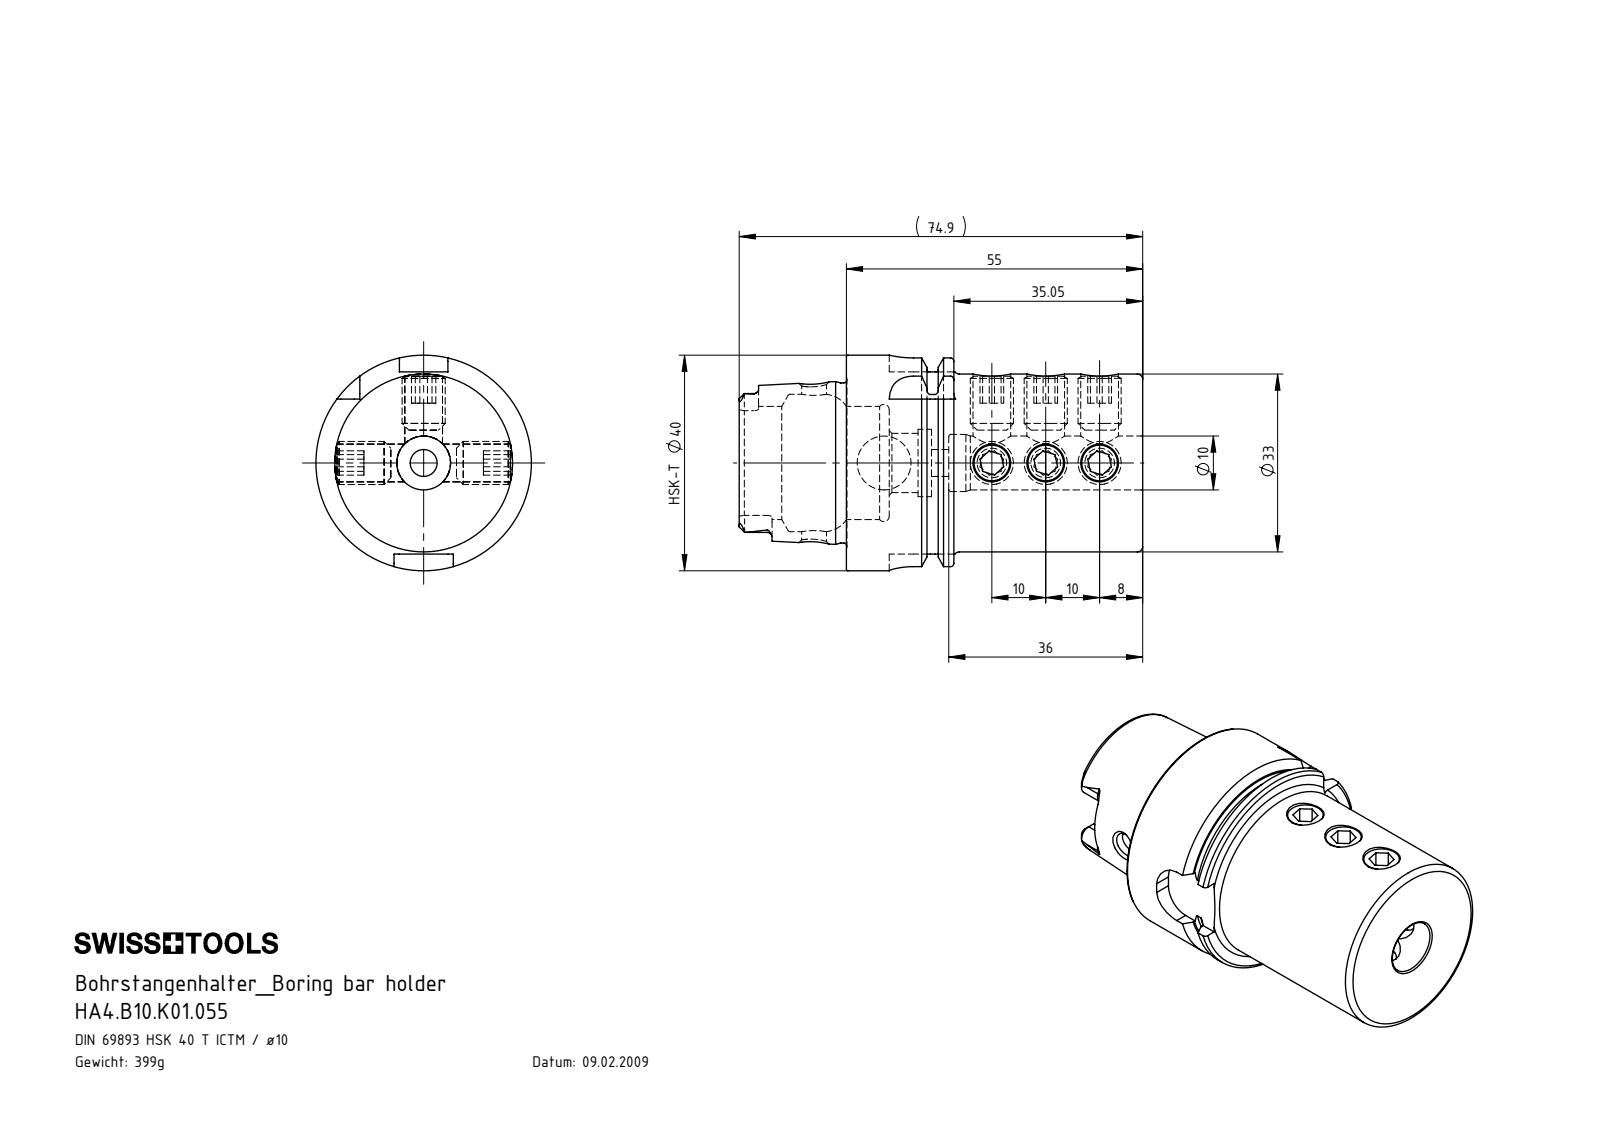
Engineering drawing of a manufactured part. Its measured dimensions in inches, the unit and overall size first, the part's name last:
Units: inches
Overall size (bounding box): 2.949 × 1.575 × 1.575
Round holes (diameter × count): ⌀0.276 ×6, ⌀0.394 ×2, ⌀0.181 ×1, ⌀0.197 ×1, ⌀0.417 ×1, ⌀0.433 ×1, ⌀0.492 ×1, ⌀0.827 ×1, ⌀1.004 ×1
Round bosses / shafts (diameter × count): ⌀0.315 ×6, ⌀1.575 ×1, ⌀1.368 ×1, ⌀1.299 ×1, ⌀1.17 ×1
Partial cylindrical surfaces — rounded edges, fillets, slot ends (radius × count): R0.035 ×6, R0.074 ×4, R0.177 ×4
Main face-to-face distances: 2.165, 0.157, 0.197, 0.394, 0.313, 1.852, 0.785, 0.472, 1.38, 0.873
Hole centre spacings: 0.394, 0.787, 1.181, 1.299, 1.575, 1.693, 2.087
Volume: 3.102 in³ · Surface area: 30.09 in²
Bodies: 10 solids, 319 faces (128 planar, 86 cylindrical, 105 other)
Part name (STEP PRODUCT): ISO 4026 - M8 x 10_PreviewCfg; HA4.B10.K01.055; HA4-B10.K01.055_C_Fertigbearbeitung
STEP written by: SolidWorks 2017 (AUTOMOTIVE_DESIGN)
